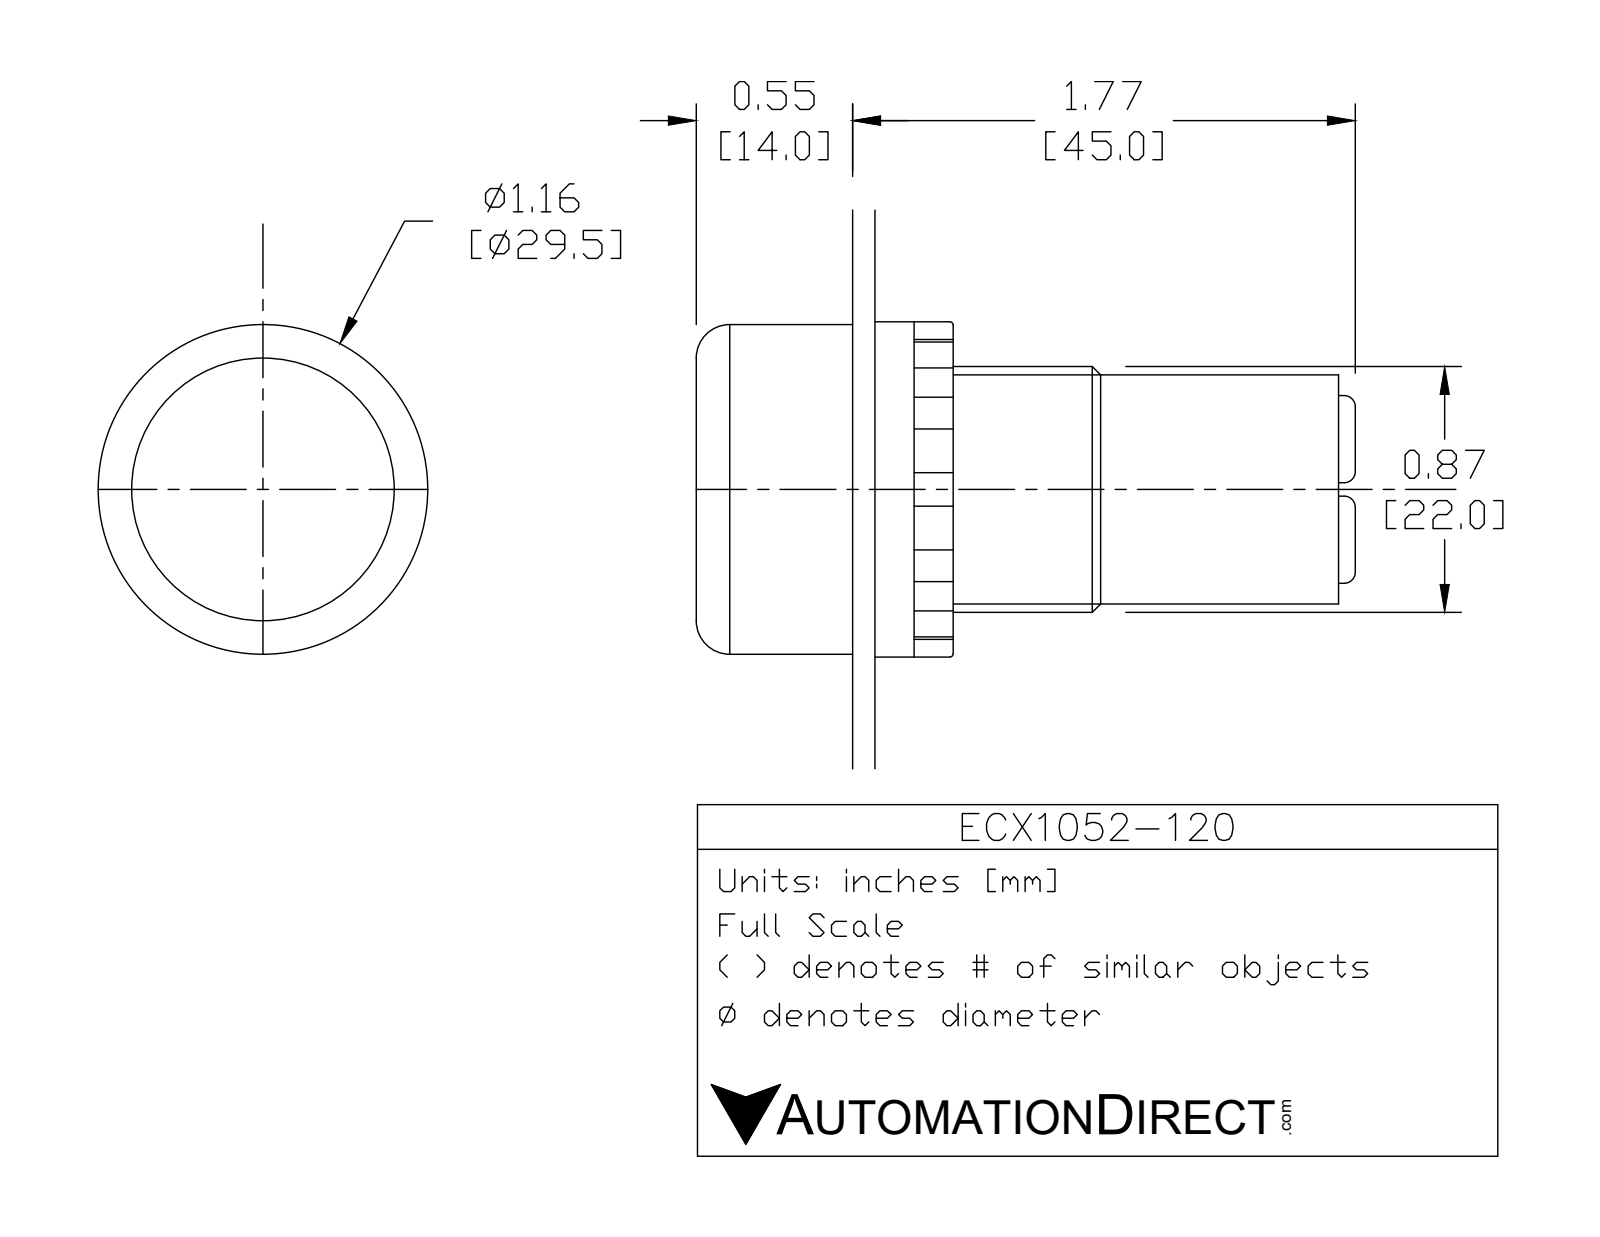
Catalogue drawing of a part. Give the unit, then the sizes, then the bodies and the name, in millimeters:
Units: millimetres
Overall size (bounding box): 59 × 30 × 30
Round holes (diameter × count): ⌀5.5 ×2, ⌀22.5 ×1
Round bosses / shafts (diameter × count): ⌀4 ×2, ⌀30 ×1, ⌀29 ×1, ⌀26.5 ×1, ⌀22 ×1, ⌀20 ×1
Partial cylindrical surfaces — rounded edges, fillets, slot ends (radius × count): R1 ×12, R9 ×1
Main face-to-face distances: 13.5, 0.5, 14, 20, 6, 6.5, 39, 7, 13, 27
Hole centre spacings: 4.62, 9.24
Volume: 26 294 mm³ · Surface area: 9 700 mm²
Bodies: 6 solids, 125 faces (63 planar, 41 cylindrical, 21 other)
Part name (STEP PRODUCT): ECX1052-120
STEP written by: SolidWorks 2017 (AUTOMOTIVE_DESIGN)
